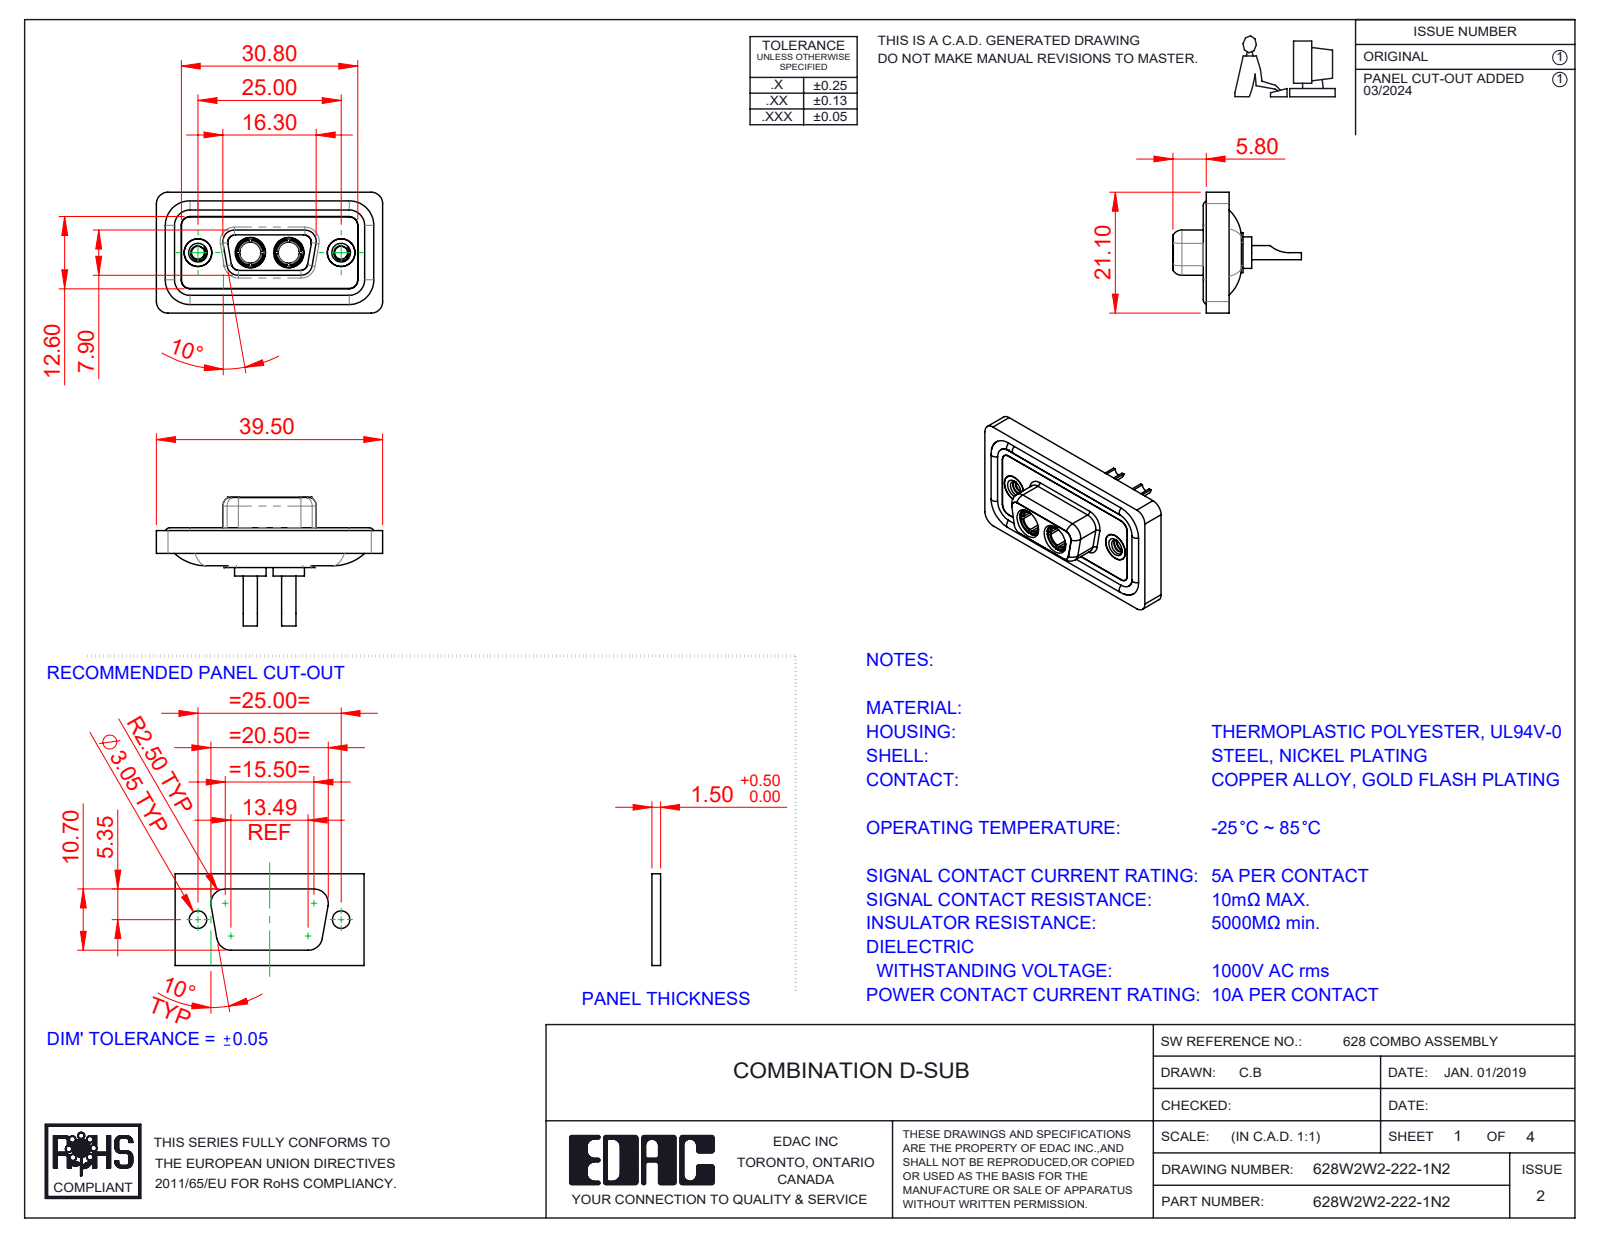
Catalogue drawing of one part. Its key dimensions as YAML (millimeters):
part_name: "628Combo Shell Front_09 Contacts; 628Combo Housing_2W2; Power Socket_10A SC; 628Combo Shell Rear_09 Contacts (+3 more)"
step_written_by: "SolidWorks 2023 (CONFIG_CONTROL_DESIGN)"
units: millimeters
bodies: {solids: 11, faces: 544, planar: 167, cylindrical: 240, other: 137}
overall_size: [39.5, 22.45, 21.1]
volume: 4707
surface_area: 7731
round_holes:
  - {diameter: 4.85, count: 4}
  - {diameter: 1.7, count: 2}
  - {diameter: 2.26, count: 2}
  - {diameter: 3.7, count: 2}
  - {diameter: 4, count: 2}
  - {diameter: 4.05, count: 2}
  - {diameter: 5, count: 2}
  - {diameter: 5.3, count: 2}
round_bosses_or_shafts:
  - {diameter: 1.6, count: 4}
  - {diameter: 5.5, count: 2}
  - {diameter: 5.2, count: 2}
  - {diameter: 4.96, count: 2}
  - {diameter: 4.95, count: 2}
  - {diameter: 4.8, count: 2}
  - {diameter: 4.75, count: 2}
  - {diameter: 3.75, count: 2}
partial_cylinders:
  - {radius: 1.5, count: 22}
  - {radius: 2, count: 18}
  - {radius: 1.35, count: 8}
  - {radius: 1.6, count: 8}
  - {radius: 0.25, count: 4}
  - {radius: 0.5, count: 4}
  - {radius: 0.6, count: 4}
  - {radius: 0.65, count: 4}
face_to_face_distances: [0.4, 1.8, 1.1, 2.9, 0.5, 1.6, 5.65, 7.45, 1.5, 5.35]
hole_center_spacings: [9.14, 15.86, 6.72, 25]
